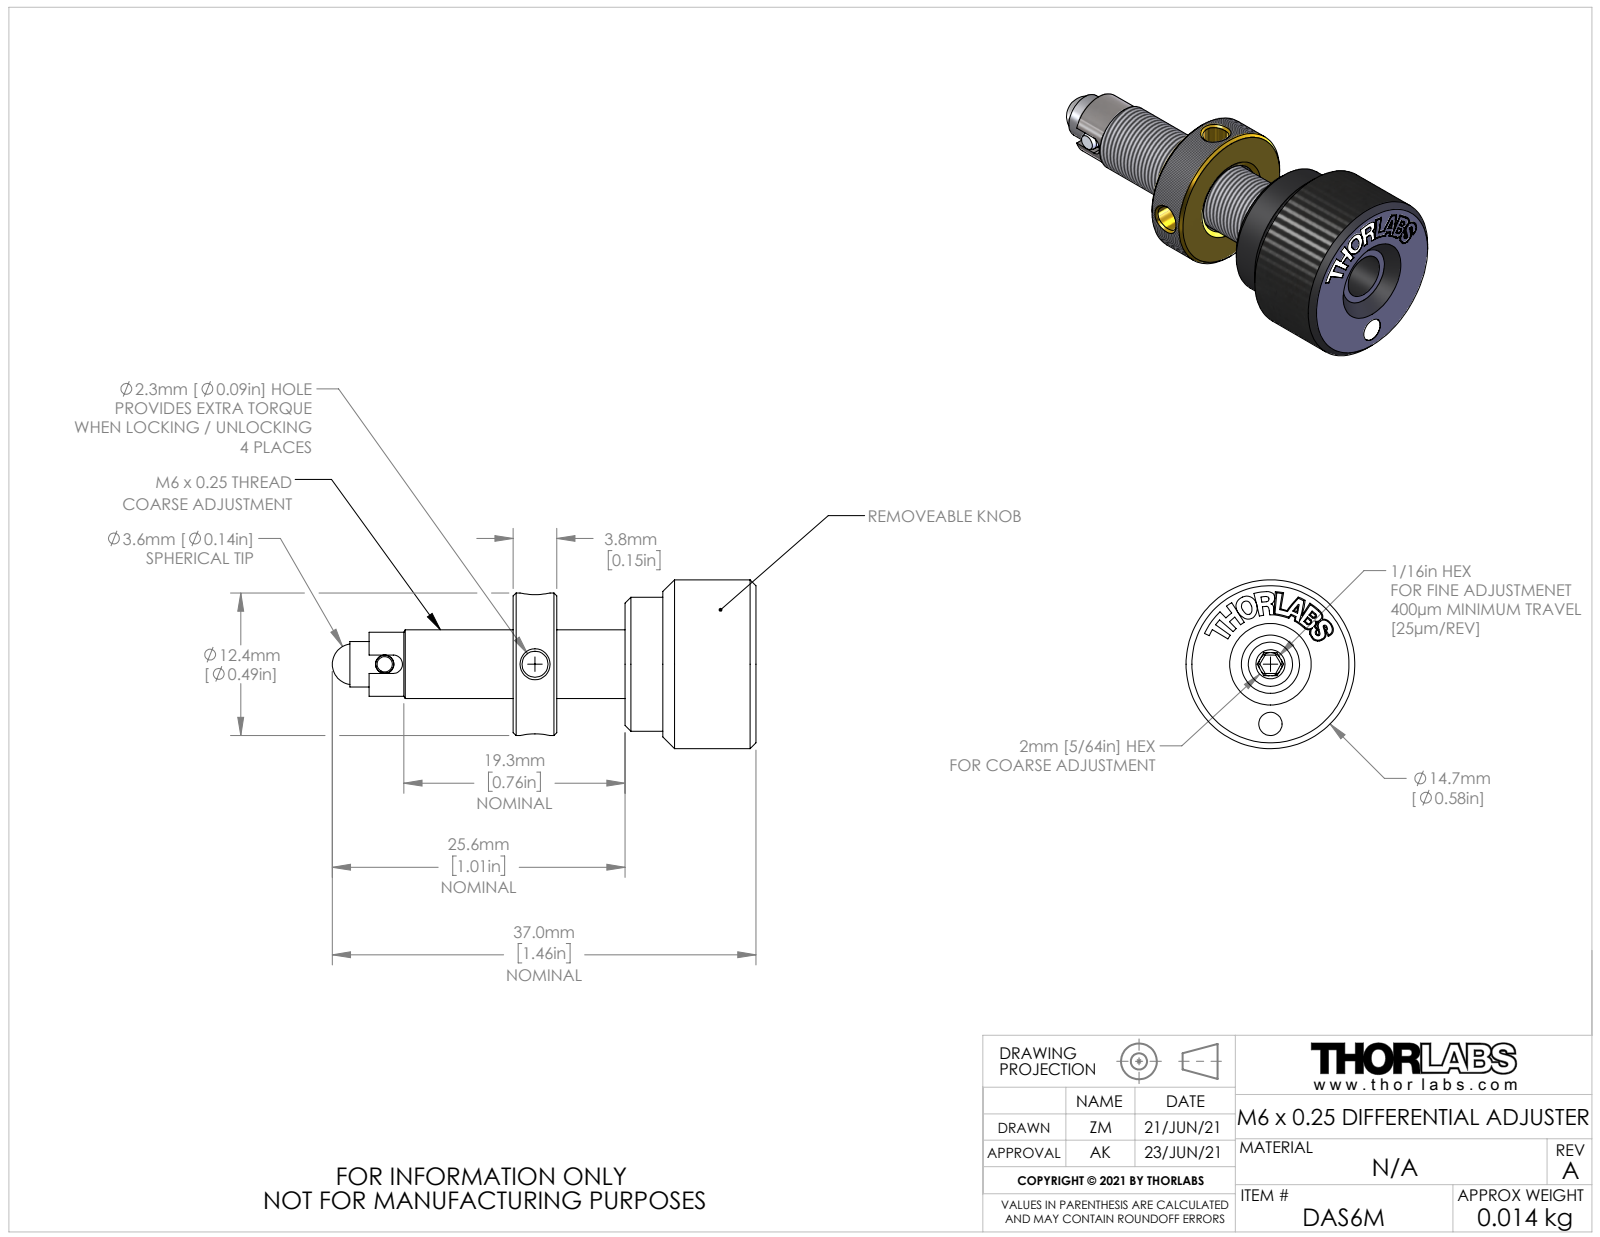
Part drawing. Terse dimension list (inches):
name: TTN253574-E0W
written by: SolidWorks 2018 (AUTOMOTIVE_DESIGN)
unit: in
bodies: 8 solids, 326 faces (93 planar, 67 cylindrical, 166 other)
size: 1.456 × 0.58 × 0.58
volume: 0.145 in³; area: 4.615 in²
holes: 2× ⌀0.09, 1× ⌀0.063, 1× ⌀0.07, 1× ⌀0.08, 1× ⌀0.098, 1× ⌀0.118, 1× ⌀0.141, 1× ⌀0.152, 1× ⌀0.157, 1× ⌀0.204, 1× ⌀0.245, 1× ⌀0.25
bosses: 1× ⌀0.58, 1× ⌀0.49, 1× ⌀0.46, 1× ⌀0.236, 1× ⌀0.22, 1× ⌀0.203, 1× ⌀0.183, 1× ⌀0.157
rounds: 1× R0.032
face distances: 0.834, 0.15, 0.684, 0.27, 0.564, 0.414, 0.384, 0.234, 0.18, 0.45
hole spacings: 0.205, 0.517
